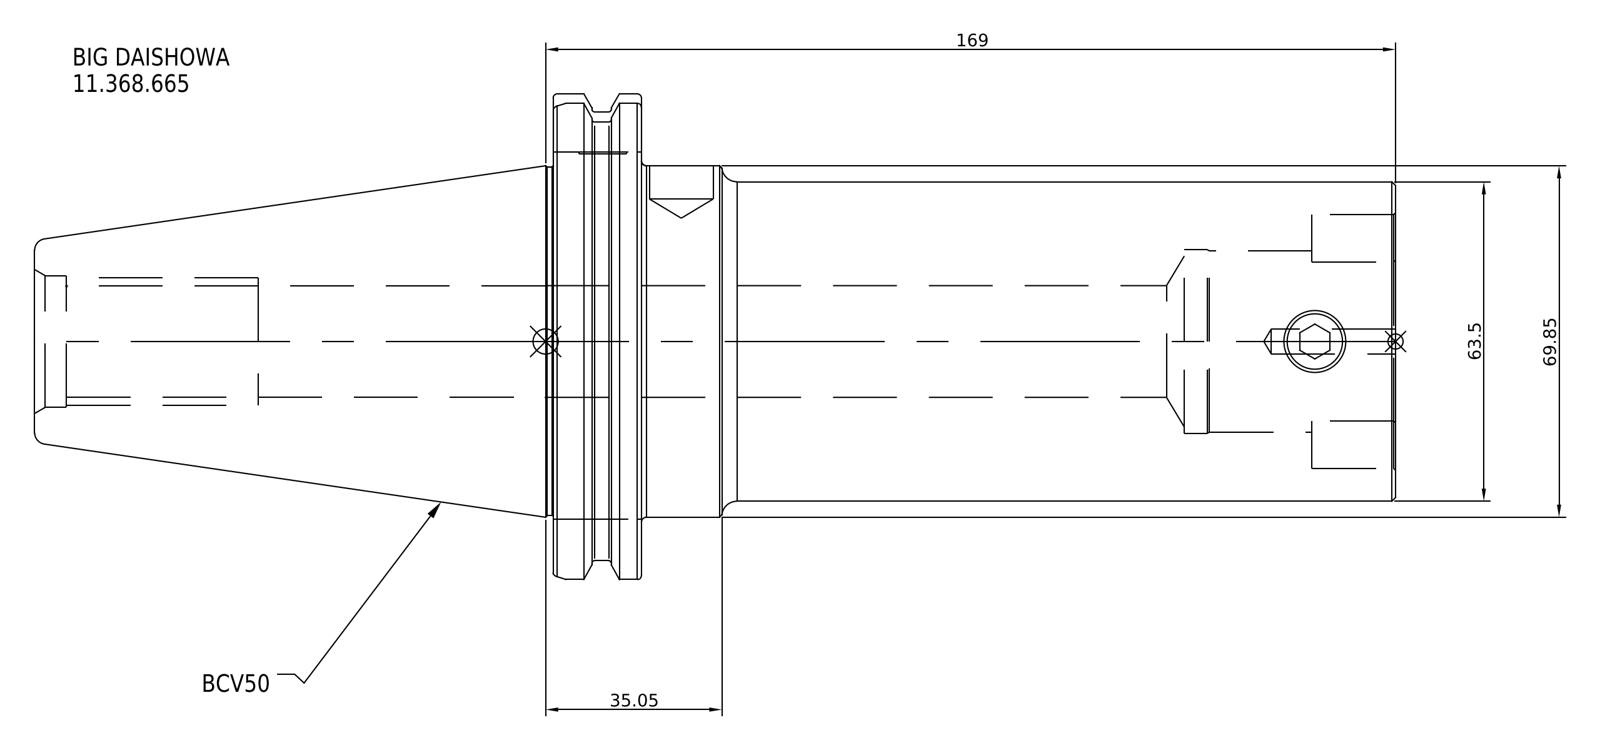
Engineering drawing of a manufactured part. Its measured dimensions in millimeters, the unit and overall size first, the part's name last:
Units: millimetres
Overall size (bounding box): 270.6 × 98.43 × 98.43
Round bosses / shafts (diameter × count): ⌀98.43 ×1, ⌀91.29 ×1, ⌀69.85 ×1, ⌀63.5 ×1
Main face-to-face distances: 17.55, 149.95, 167.5, 270.6, 120.65, 103.1, 134, 15.95, 33.5, 136.6
Volume: 866 848 mm³ · Surface area: 67 705 mm²
Bodies: 1 solid, 16 faces (7 planar, 6 cylindrical, 3 other)
Part name (STEP PRODUCT): 11.368.665
STEP written by: SolidWorks 2021 (CONFIG_CONTROL_DESIGN)
